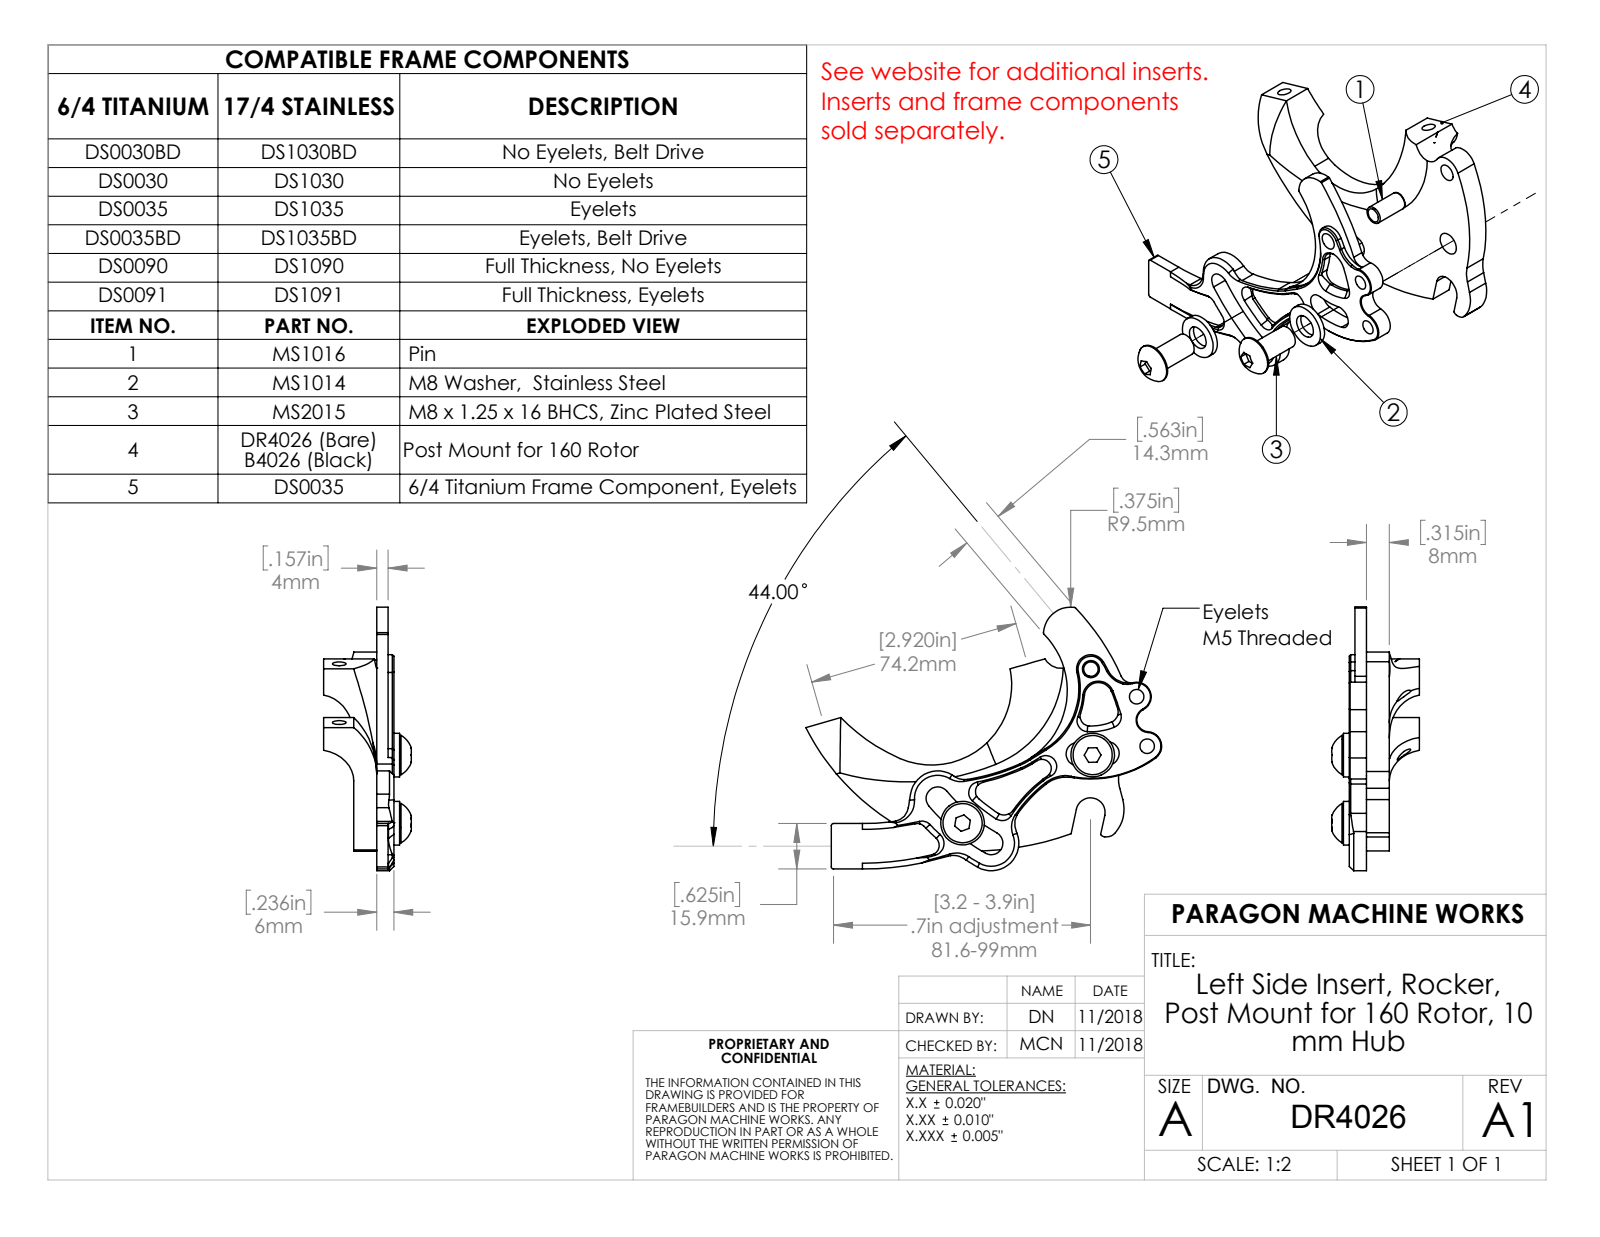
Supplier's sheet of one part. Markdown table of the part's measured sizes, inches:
| quantity | value |
| --- | --- |
| part name | DR4026 |
| STEP written by | SolidWorks 2018 (AUTOMOTIVE_DESIGN) |
| units | inches |
| bodies | 1 solid, 45 faces (9 planar, 30 cylindrical, 6 other) |
| overall size | 4.44 × 2.846 × 0.728 |
| volume | 2.053 in³ |
| surface area | 18.77 in² |
| round holes (diameter × count) | 0.187 × 2, 0.236 × 1, 0.315 × 1, 0.315 × 1 |
| partial cylindrical surfaces (radius × count) | 0.5 × 4, 0.082 × 1, 0.165 × 1, 0.2 × 1, 0.236 × 1, 0.25 × 1, 0.38 × 1, 1 × 1 |
| main face-to-face distances | 0.315, 0.413, 0.728, 0.4 |
| hole center spacings | 1.181, 2.019, 2.756, 2.92 |
